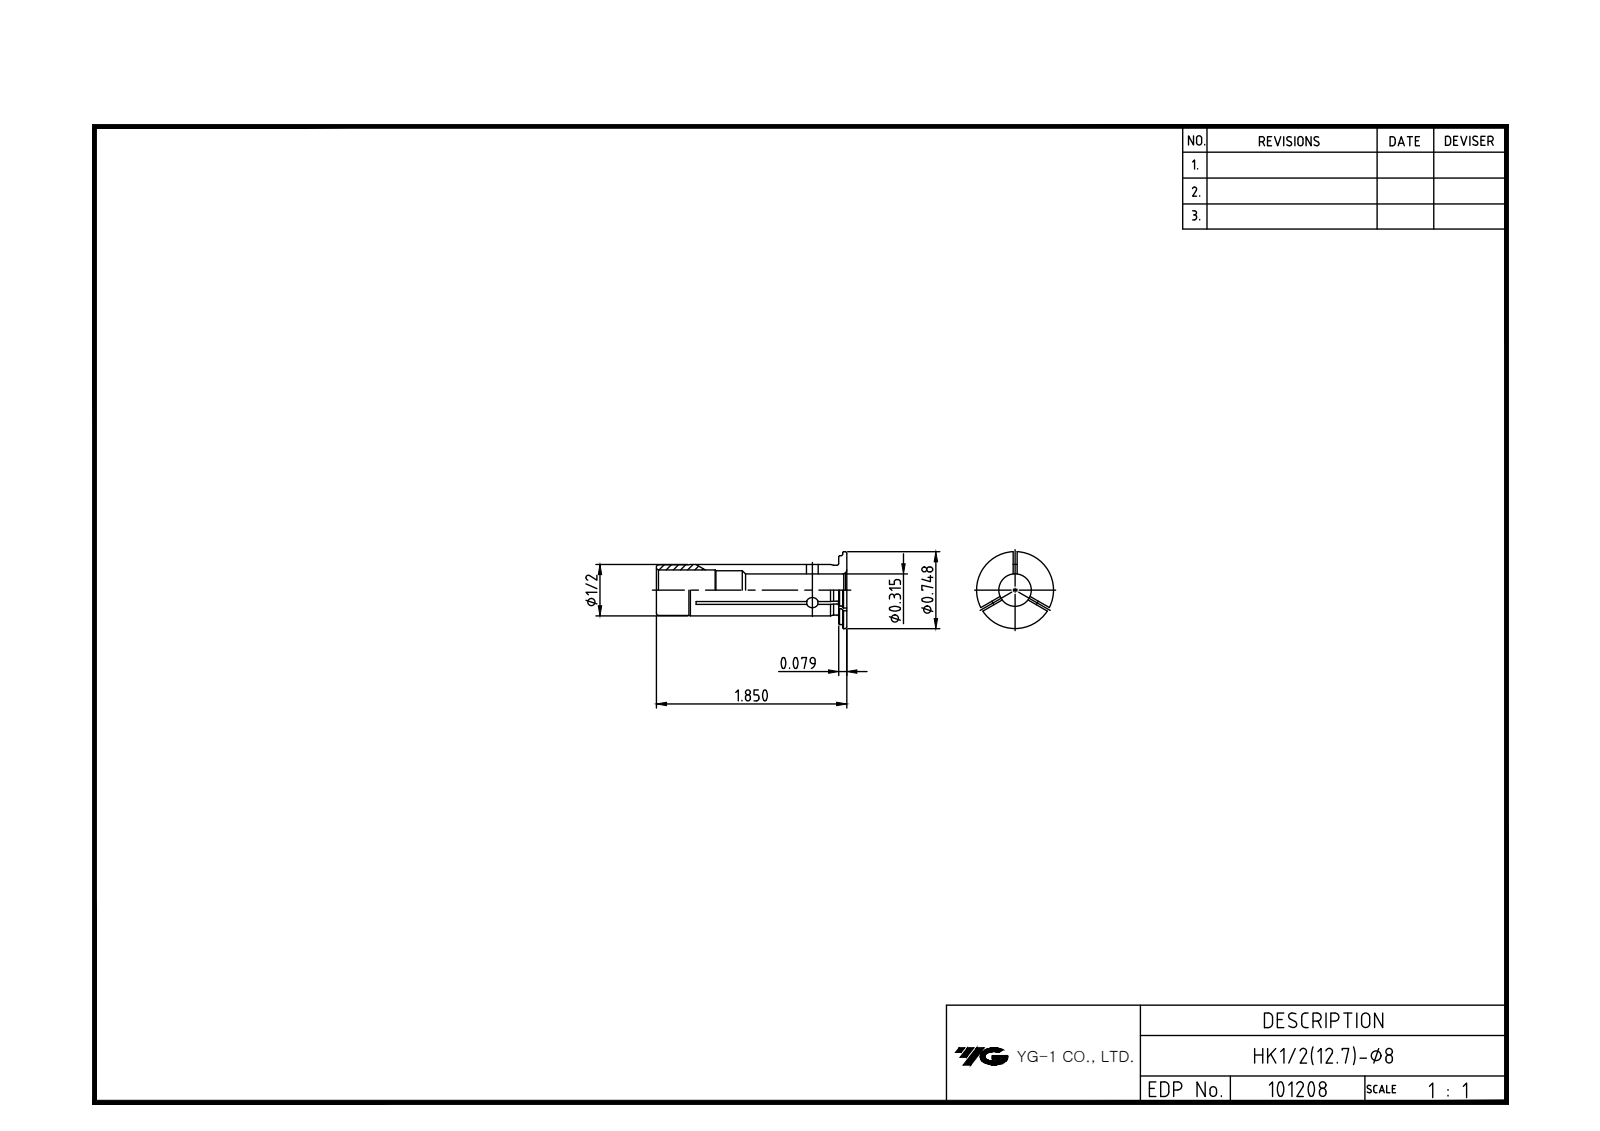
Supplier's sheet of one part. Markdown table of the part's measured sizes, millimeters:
| quantity | value |
| --- | --- |
| part name | LO-HK12.7-8 |
| STEP written by | Autodesk Inventor 2025 (AP242_MANAGED_MODEL_BASED_3D_ENGINEERING_MIM_LF) |
| units | millimeters |
| bodies | 1 solid, 12 faces (4 planar, 6 cylindrical, 2 other) |
| overall size | 47 × 19 × 19 |
| volume | 3 281 mm³ |
| surface area | 3 667 mm² |
| round holes (diameter × count) | 8 × 1, 9.6 × 1, 10 × 1 |
| round bosses / shafts (diameter × count) | 19 × 1, 17 × 1, 12.7 × 1 |
| main face-to-face distances | 1, 2, 45, 46, 47 |
